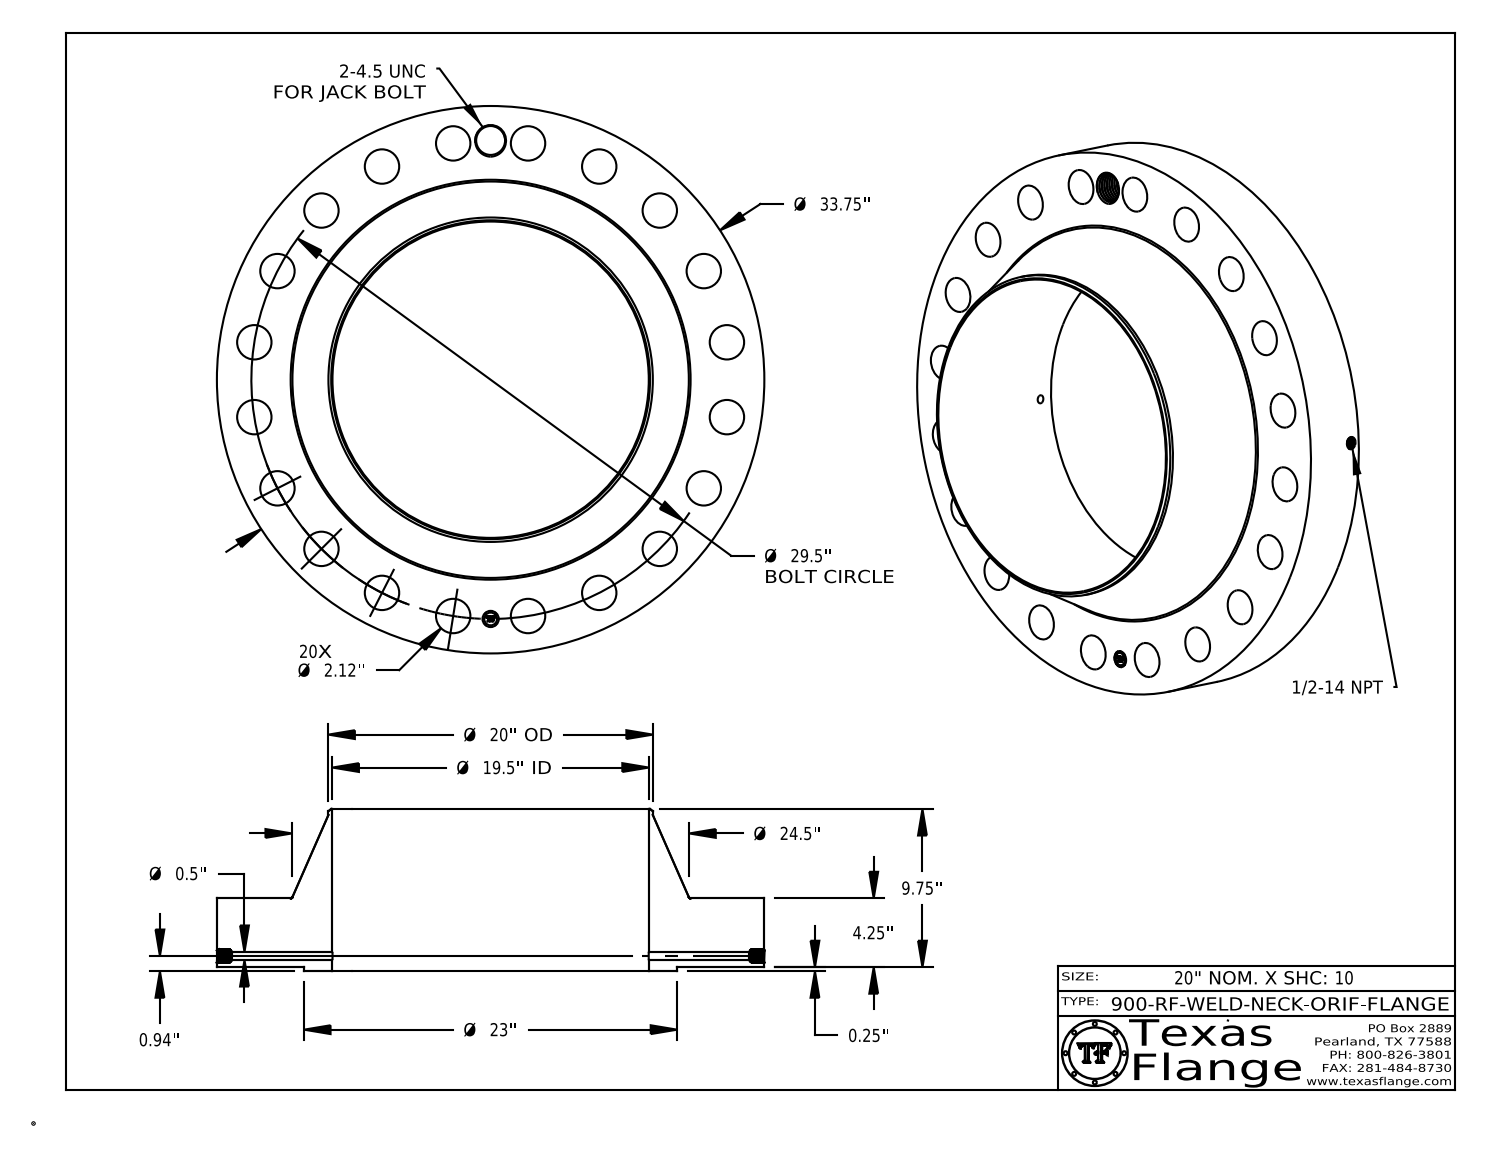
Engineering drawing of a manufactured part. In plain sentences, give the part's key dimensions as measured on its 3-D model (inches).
The part is named "900-RF-WELD-NECK". Its 3-D file was written by "CATIA V5 STEP AP214 (AUTOMOTIVE_DESIGN)". It is 1 solid with 818 faces: 369 planar, 126 cylindrical and 323 other. Overall it measures 33.75 by 33.75 by 10 inches. Its volume is 2 722 cubic inches and its surface area 3 005 square inches. Round holes: 20 of diameter 2.12, 1 of diameter 0.5, 1 of diameter 0.672, 1 of diameter 1, 1 of diameter 1.781, 1 of diameter 19.5. Round bosses or shafts: 8 of diameter 0.061, 1 of diameter 33.75, 1 of diameter 23, 1 of diameter 20, 1 of diameter 0.788. The main face-to-face distances are 4.25, 0.25, 4.5, 10, 9.75, 5.5, 4.485, 4.235, 0.015, 5.515. The hole center spacings are 4.615, 9.116, 13.393, 17.34, 20.86, 23.866, 26.285, 29.137.
